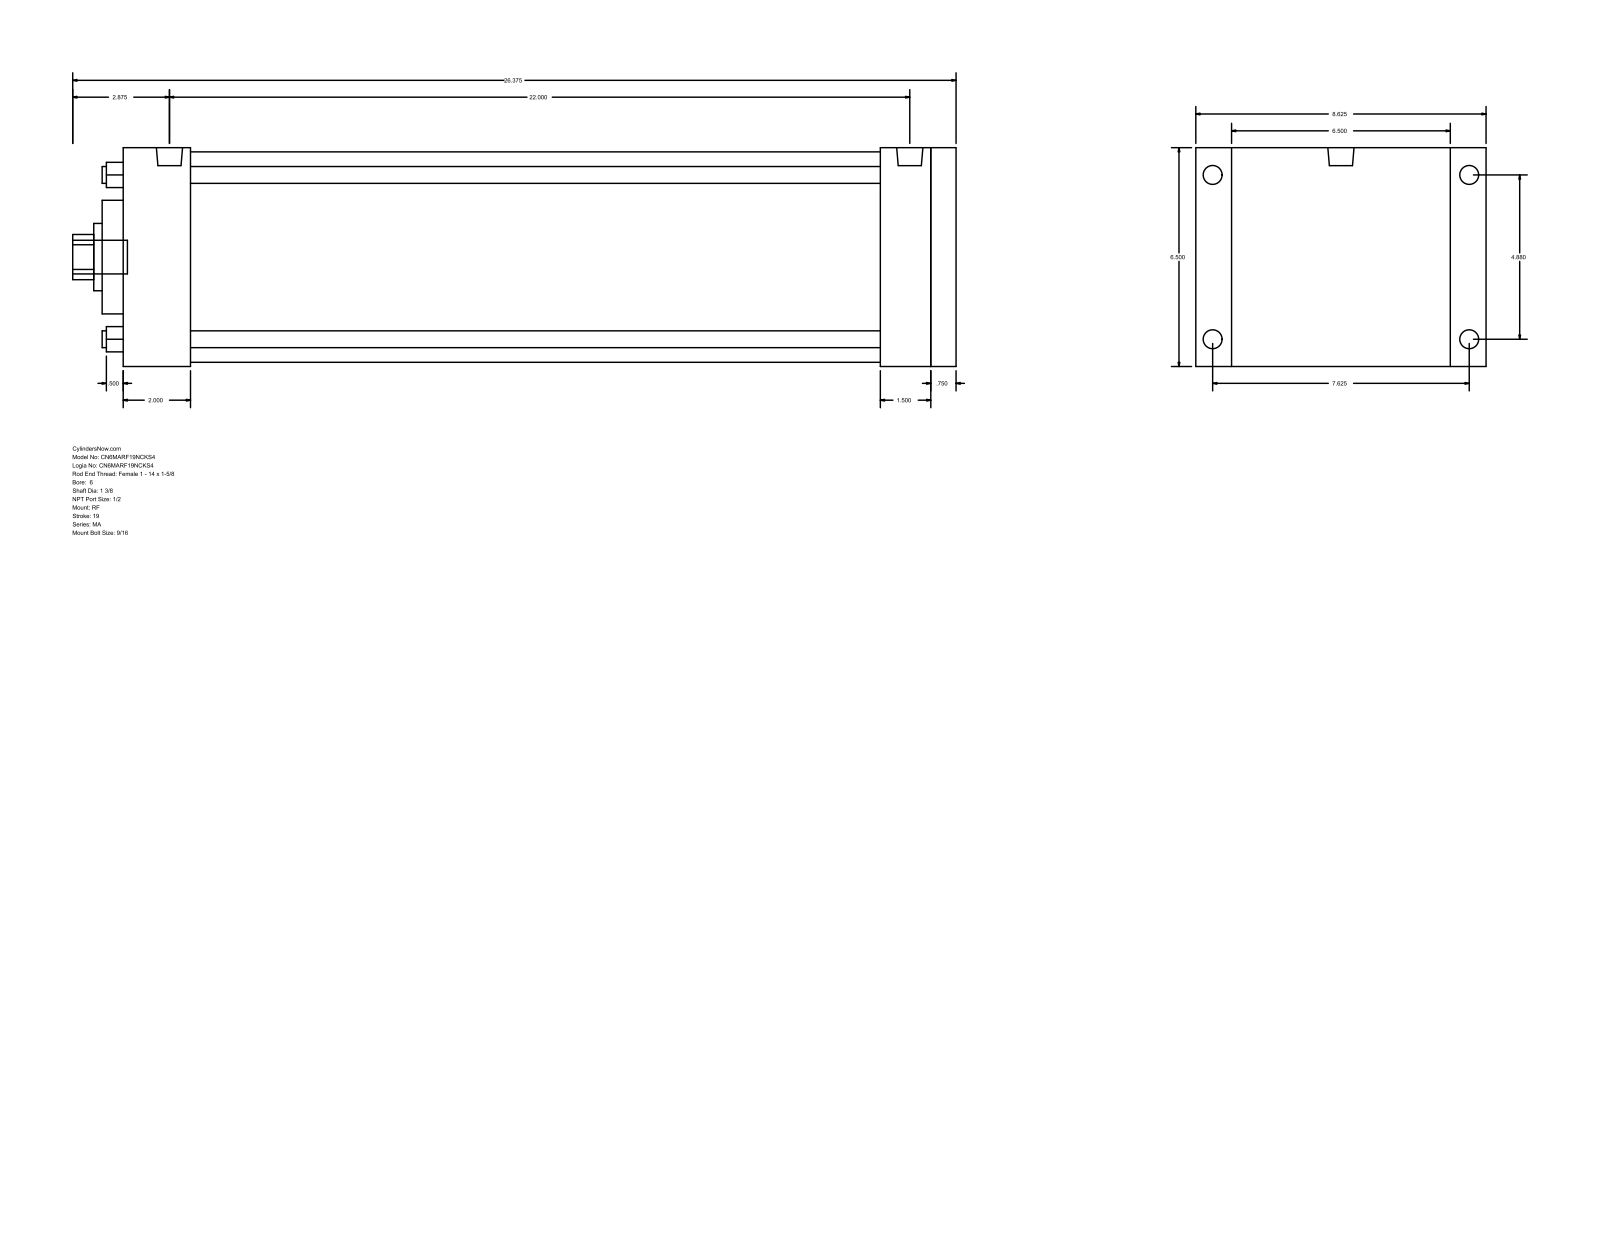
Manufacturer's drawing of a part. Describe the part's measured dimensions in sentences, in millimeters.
The part is named "MA_RF__0600_1.375". Its 3-D file was written by "GSSL Pune (CONFIG_CONTROL_DESIGN)". It is 0 solids with 94 faces: 65 planar, 29 cylindrical and 0 other. Overall it measures 669.92 by 219.07 by 165.1 millimeters. Round holes: 4 of diameter 12.7, 1 of diameter 34.92, 1 of diameter 50.8, 1 of diameter 85.72, 1 of diameter 158.75. Round bosses or shafts: 4 of diameter 17.46, 4 of diameter 14.29, 2 of diameter 19.77, 1 of diameter 25.4. Partial cylindrical surfaces (rounded edges, fillets, slot ends): 1 of radius 17.06. The main face-to-face distances are 165.1, 631.82, 19.04, 612.78, 50.8, 561.98, 581.02, 574.67, 523.87, 38.11. The hole center spacings are 87.65, 123.96, 175.31.
